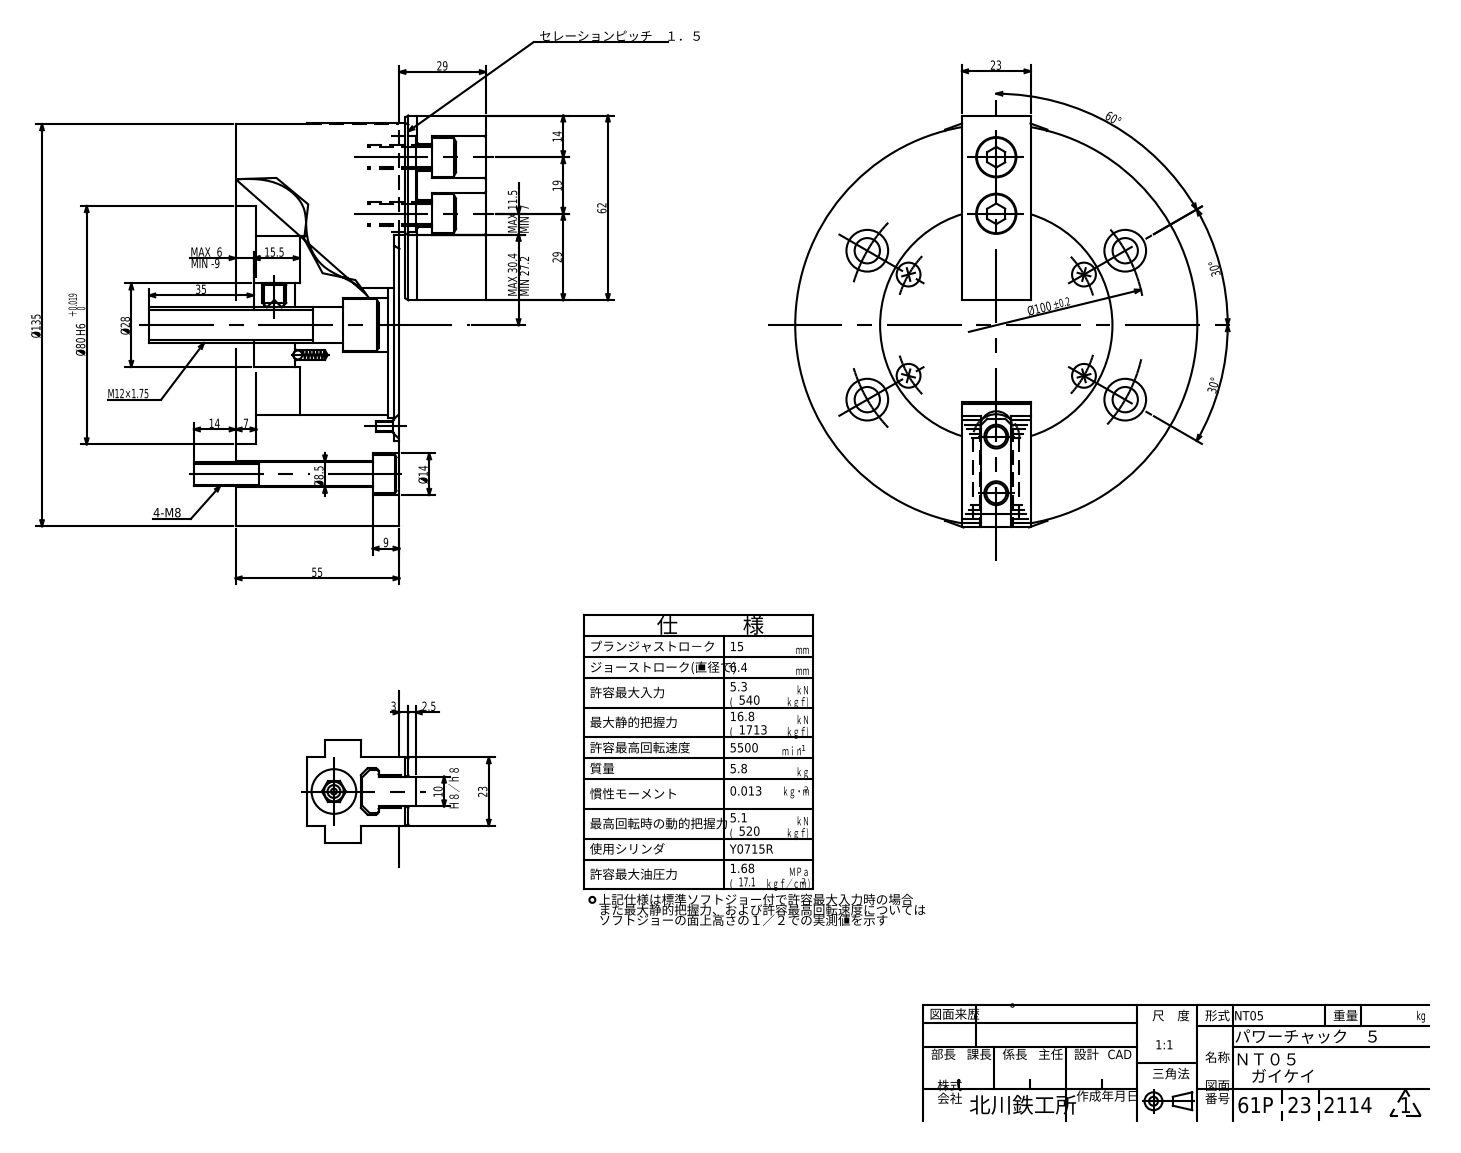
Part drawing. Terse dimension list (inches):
written by: ST-DEVELOPER v16.7 (AUTOMOTIVE_DESIGN)
unit: in
bodies: 1 solid, 583 faces (414 planar, 121 cylindrical, 48 other)
size: 5.543 × 5.315 × 4.449
volume: 47.7 in³; area: 175.2 in²
holes: 8× ⌀0.335, 4× ⌀0.268, 4× ⌀0.531, 4× ⌀0.551, 2× ⌀0.433, 1× ⌀0.075, 1× ⌀0.591, 1× ⌀0.709, 1× ⌀2.346, 1× ⌀3.15
bosses: 12× ⌀0.315, 8× ⌀0.512, 2× ⌀0.394, 2× ⌀0.236, 1× ⌀5.315, 1× ⌀1.102, 1× ⌀0.689, 1× ⌀0.472
rounds: 8× R0.079, 4× R0.024, 4× R0.065, 2× R0.039, 2× R0.215, 2× R0.305, 1× R1.181, 1× R1.22
face distances: 2.165, 1.142, 0.079, 0.906, 0.236, 1.22, 0.157, 0.276, 1.299, 2.008
hole spacings: 1.969, 1.773, 1.921, 2.106, 2.99, 3.325, 3.63, 0.35
